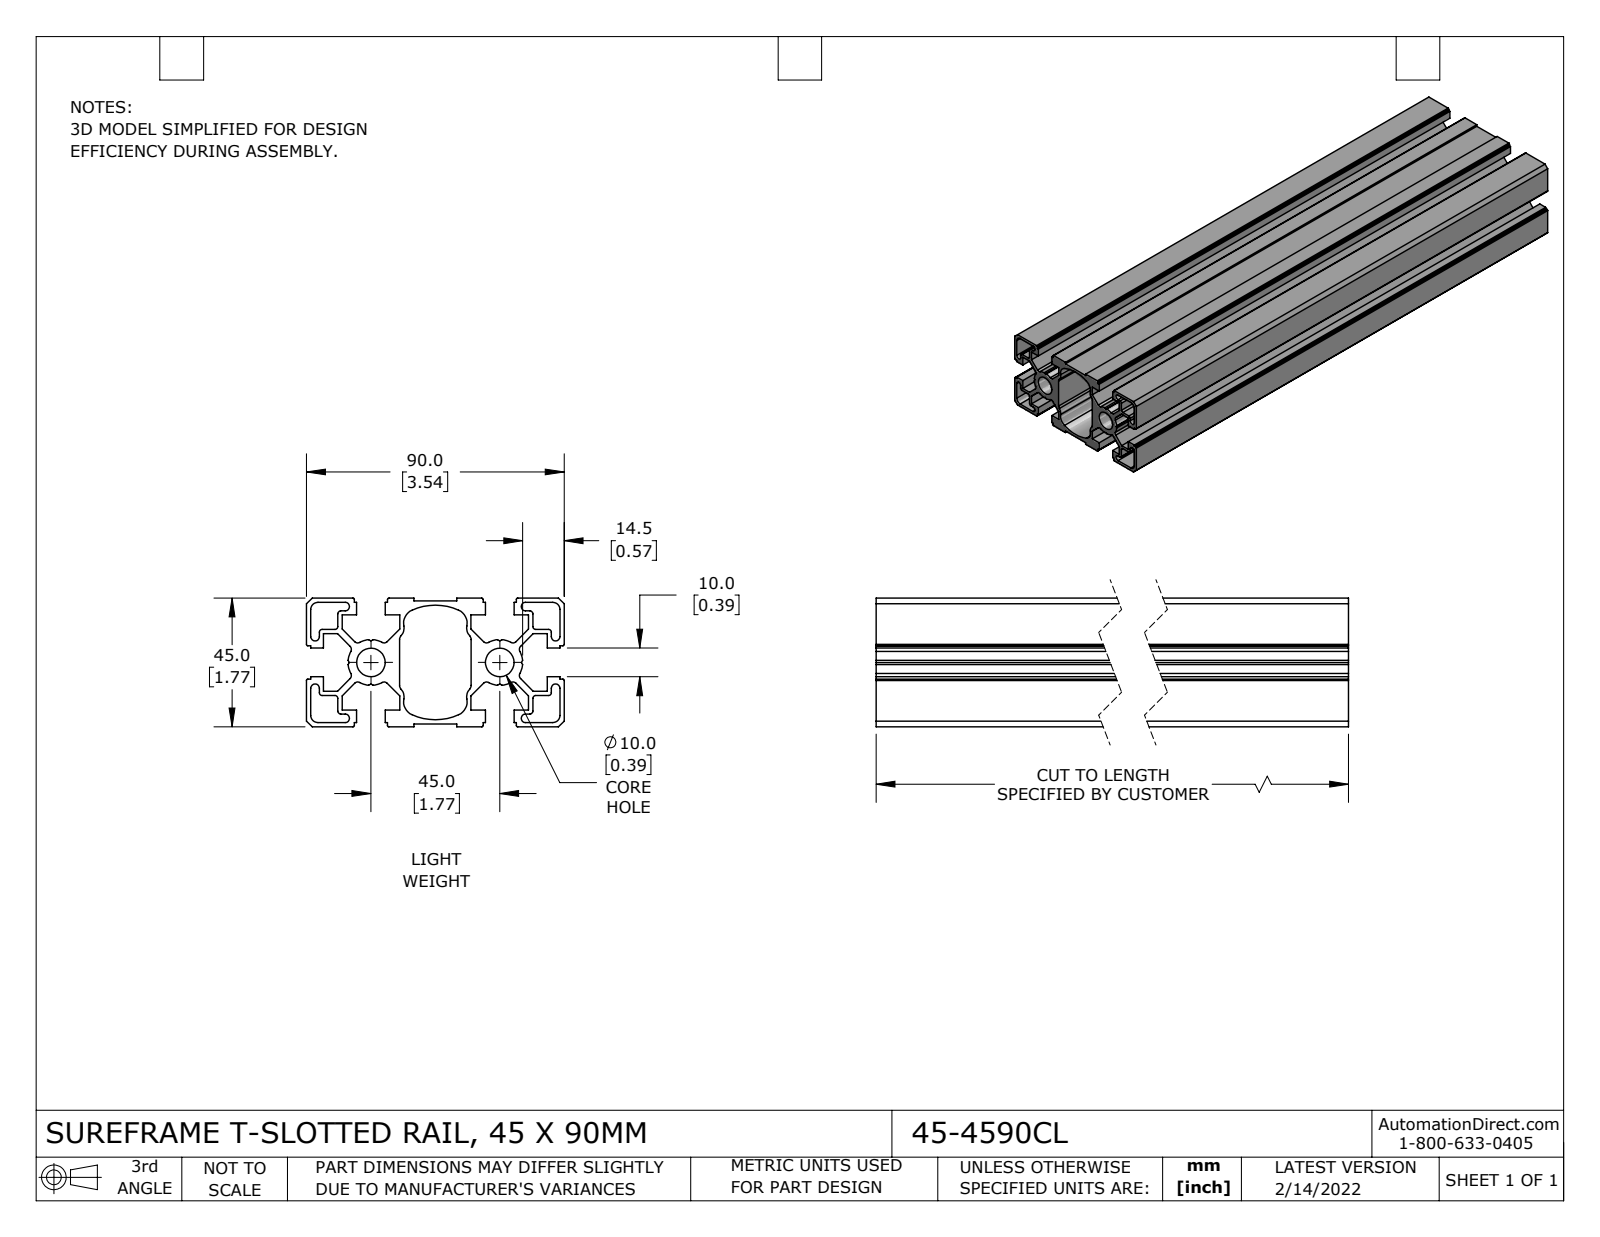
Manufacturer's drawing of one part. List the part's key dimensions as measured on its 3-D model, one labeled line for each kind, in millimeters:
Part name (STEP PRODUCT): 45-4590CL
STEP written by: SolidWorks 2021 (CONFIG_CONTROL_DESIGN)
Units: millimetres
Bodies: 1 solid, 218 faces (134 planar, 84 cylindrical, 0 other)
Overall size (bounding box): 304.8 × 90 × 45
Volume: 352 954 mm³ · Surface area: 281 815 mm²
Round holes (diameter × count): ⌀10 ×2
Partial cylindrical surfaces — rounded edges, fillets, slot ends (radius × count): R1.5 ×20, R0.5 ×12, R1 ×12, R2 ×4, R2.5 ×4, R4 ×4, R5 ×4, R8 ×2
Main face-to-face distances: 1.5, 45, 5.05, 10.95, 6.55, 21.6, 32.55, 15.05, 43.5, 88.5
Hole centre spacings: 45
